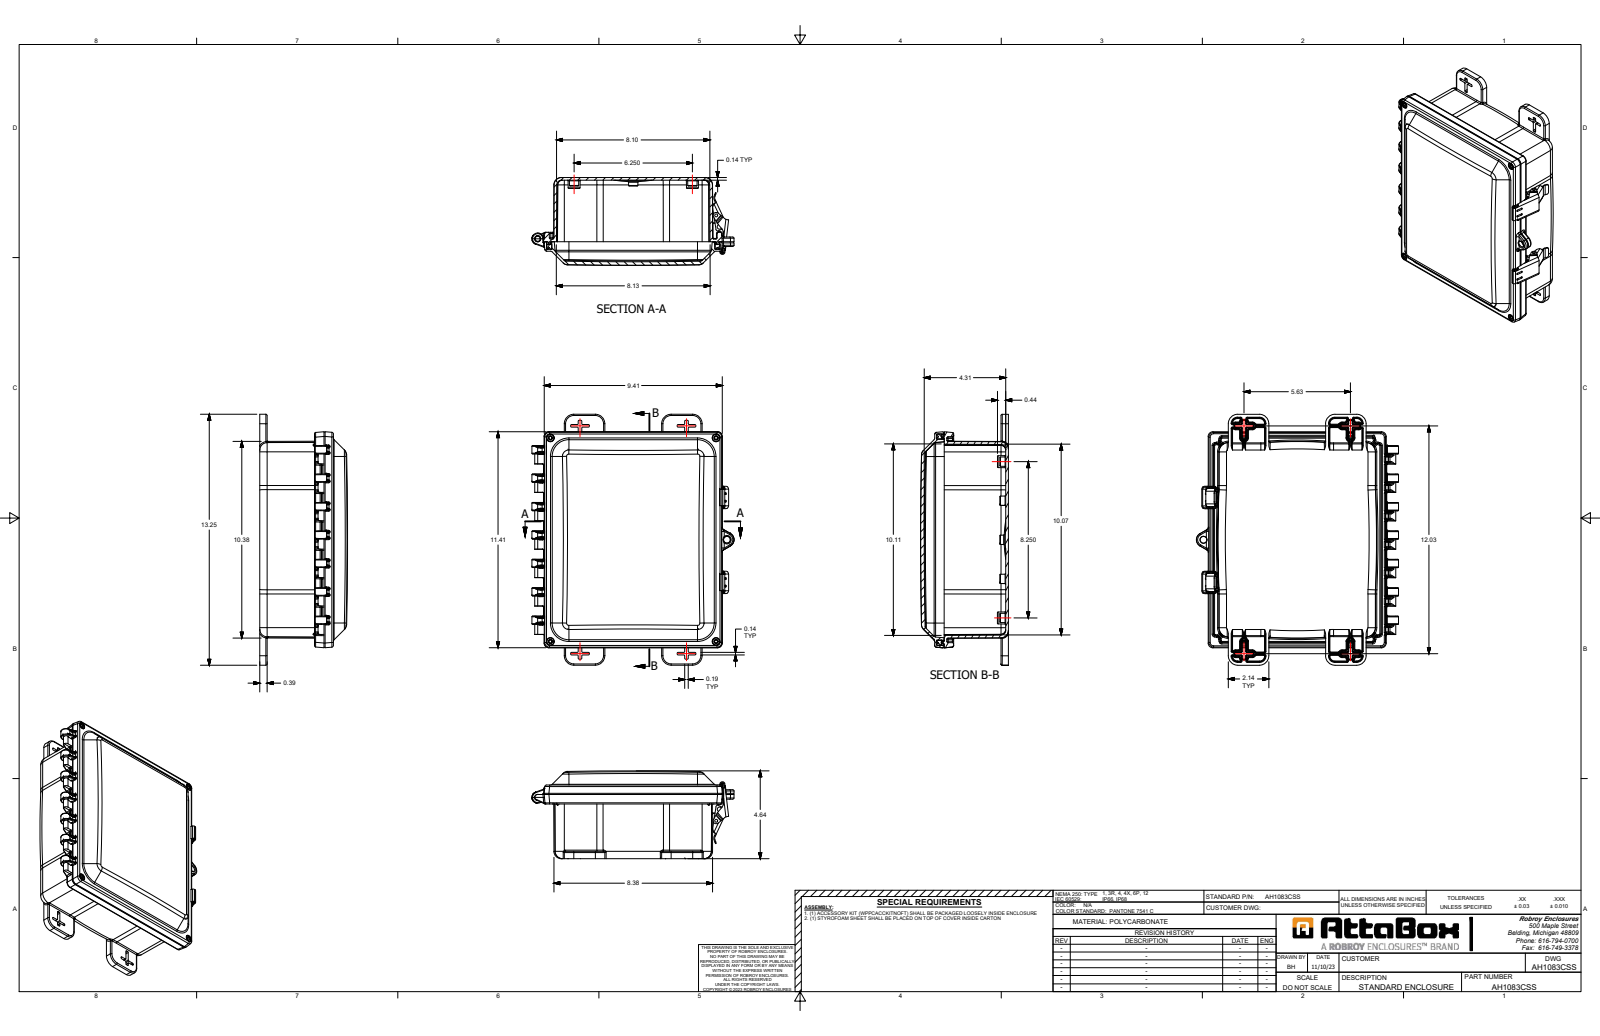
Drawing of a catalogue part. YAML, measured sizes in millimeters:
part_name: "AH1083C"
step_written_by: "SolidWorks 2023 (AUTOMOTIVE_DESIGN)"
units: millimeters
bodies: {solids: 6, faces: 1801, planar: 487, cylindrical: 570, other: 744}
overall_size: [336.6, 271.2, 119.5]
volume: 1251000
surface_area: 560100
round_holes:
  - {diameter: 4.5, count: 11}
  - {diameter: 5, count: 4}
  - {diameter: 7.3, count: 4}
  - {diameter: 7.5, count: 4}
  - {diameter: 9.9, count: 4}
  - {diameter: 8.3, count: 1}
  - {diameter: 9.5, count: 1}
  - {diameter: 11.4, count: 1}
round_bosses_or_shafts:
  - {diameter: 12.6, count: 11}
  - {diameter: 16.2, count: 4}
  - {diameter: 8, count: 1}
partial_cylinders:
  - {radius: 0.9, count: 128}
  - {radius: 1.7, count: 85}
  - {radius: 0.6, count: 26}
  - {radius: 0.3, count: 25}
  - {radius: 0.5, count: 16}
  - {radius: 12.7, count: 12}
  - {radius: 3.3, count: 9}
  - {radius: 3.2, count: 8}
face_to_face_distances: [2.8, 86.1, 83.3, 12.7, 3.4, 73.4, 70.6, 3.8, 203.1, 8.9]
hole_center_spacings: [79.4, 95.1, 131.3, 44.9, 52.3, 95.1, 104.6, 158.8]
